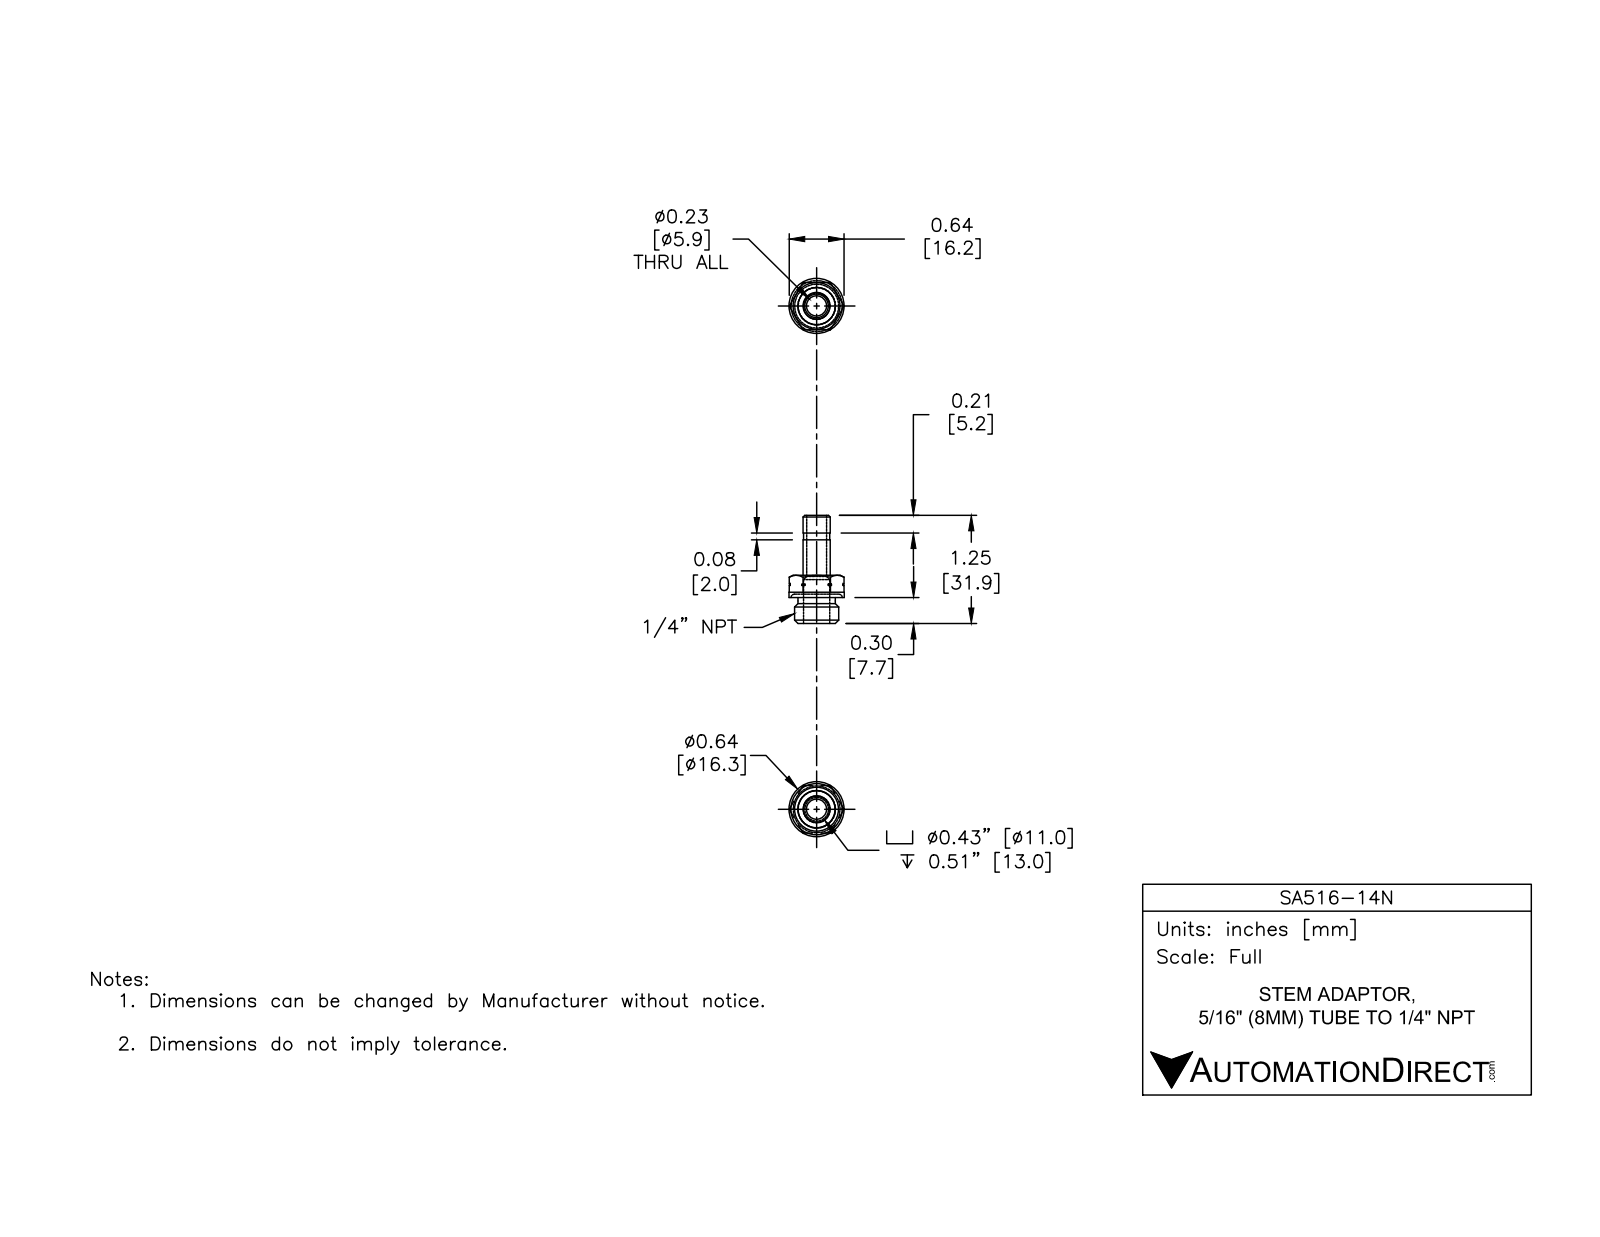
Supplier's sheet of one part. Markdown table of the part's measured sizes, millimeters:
| quantity | value |
| --- | --- |
| part name | SA516-14N |
| STEP written by | SolidWorks 2015 (CONFIG_CONTROL_DESIGN) |
| units | millimeters |
| bodies | 2 solids, 61 faces (13 planar, 22 cylindrical, 26 other) |
| overall size | 31.88 × 16.25 × 16.25 |
| volume | 1 947 mm³ |
| surface area | 2 357 mm² |
| round holes (diameter × count) | 5.9 × 1, 7.77 × 1 |
| round bosses / shafts (diameter × count) | 16.25 × 1, 12.97 × 1, 11 × 1, 8 × 1, 7.75 × 1 |
| partial cylindrical surfaces (radius × count) | 7.8 × 1 |
| main face-to-face distances | 14, 6.6, 7.65, 14.25, 9.25, 1.6, 5, 31.87, 24.22, 22.62 |
